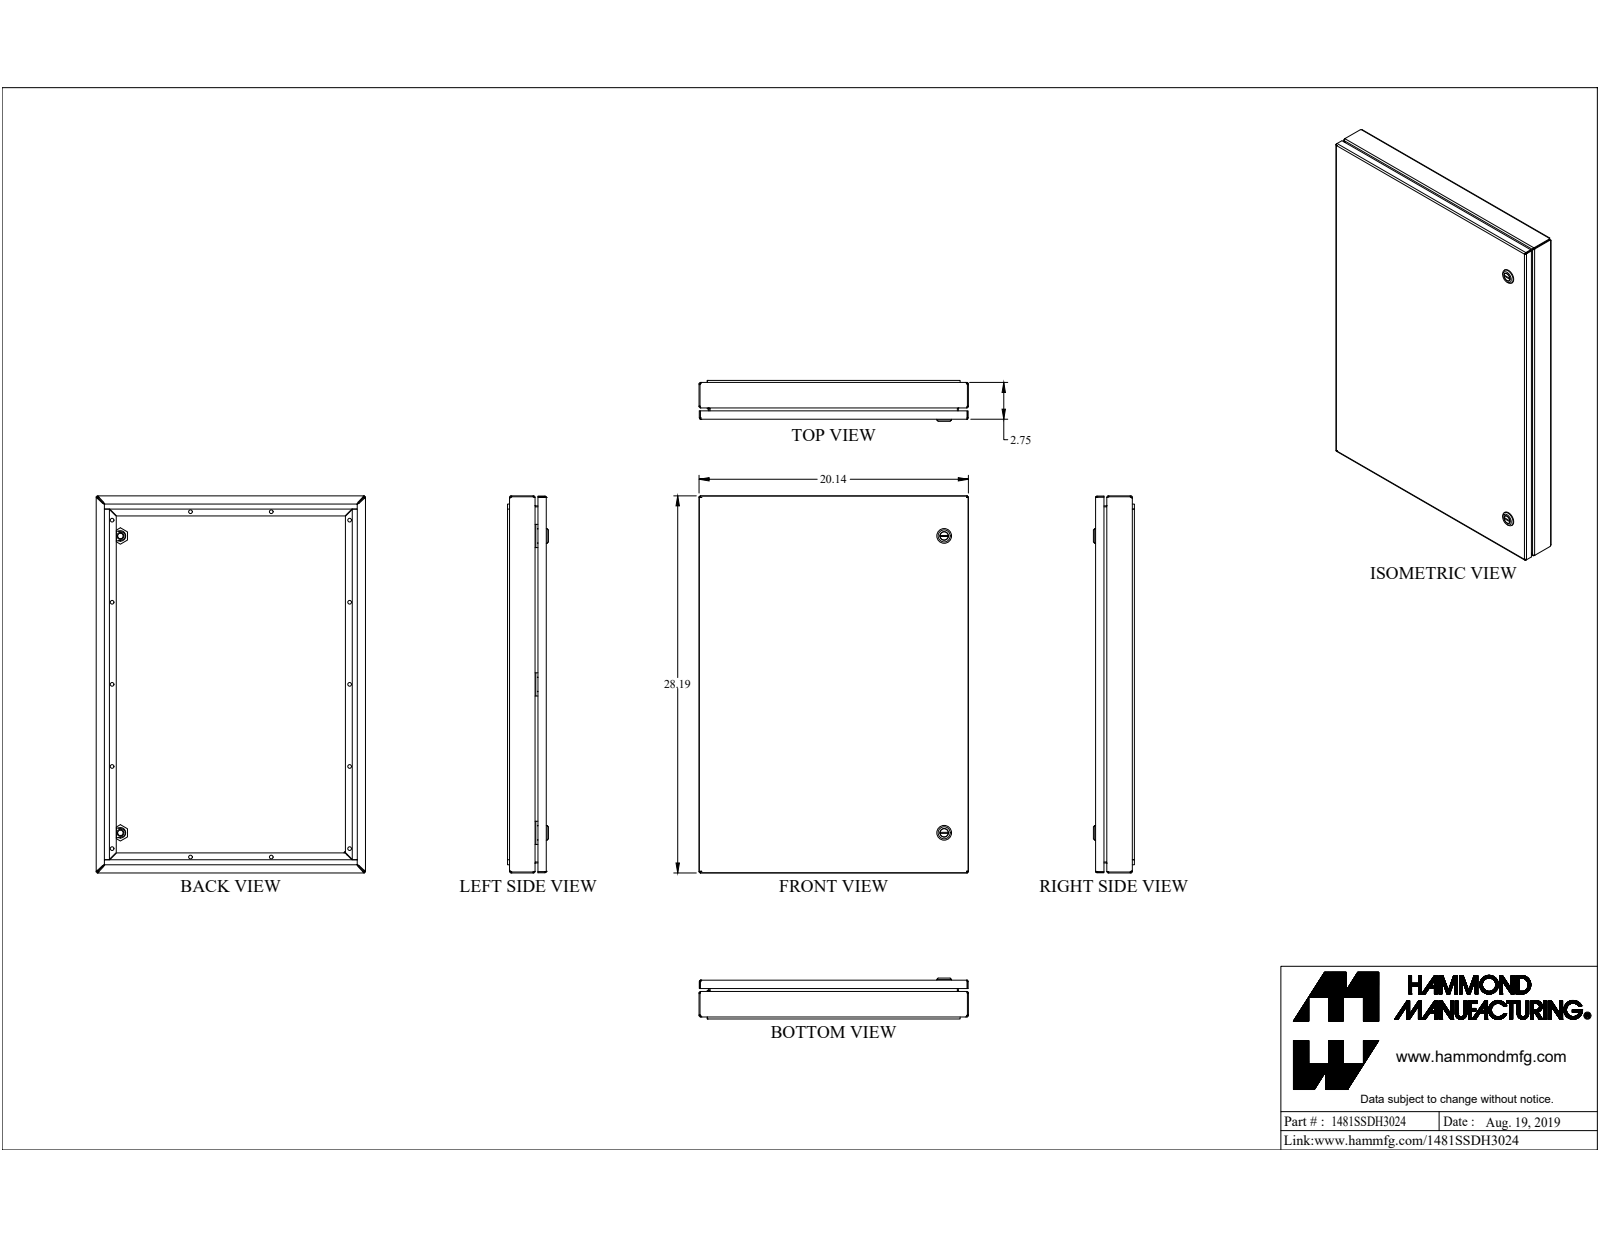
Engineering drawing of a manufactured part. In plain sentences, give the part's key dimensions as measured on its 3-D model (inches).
The part is named "1481SSDH3024". Its 3-D file was written by "SolidWorks 2019 (CONFIG_CONTROL_DESIGN)". It is 33 solids with 792 faces: 485 planar, 195 cylindrical and 112 other. Overall it measures 28.19 by 20.14 by 3.06 inches. Its volume is 95.46 cubic inches and its surface area 2 504 square inches. Round holes: 14 of diameter 0.281, 2 of diameter 0.197, 2 of diameter 0.387, 2 of diameter 0.5, 2 of diameter 0.63, 2 of diameter 0.768, 1 of diameter 0.172, 1 of diameter 0.24, 1 of diameter 0.242. Round bosses or shafts: 2 of diameter 1.1, 2 of diameter 0.785, 2 of diameter 0.625, 2 of diameter 0.525, 2 of diameter 0.236, 1 of diameter 0.475, 1 of diameter 0.398, 1 of diameter 0.356. Partial cylindrical surfaces (rounded edges, fillets, slot ends): 28 of radius 0.036, 28 of radius 0.108, 6 of radius 0.006, 6 of radius 0.062, 4 of radius 0.125, 4 of radius 0.25, 4 of radius 0.499, 2 of radius 0.307. The main face-to-face distances are 0.072, 2.578, 0.842, 1.736, 2.65, 20.068, 2.506, 2.678, 1.836, 0.1. The hole center spacings are 6.137, 18.794, 12.274, 21.592, 17.764, 5.893, 11.922, 18.411.
